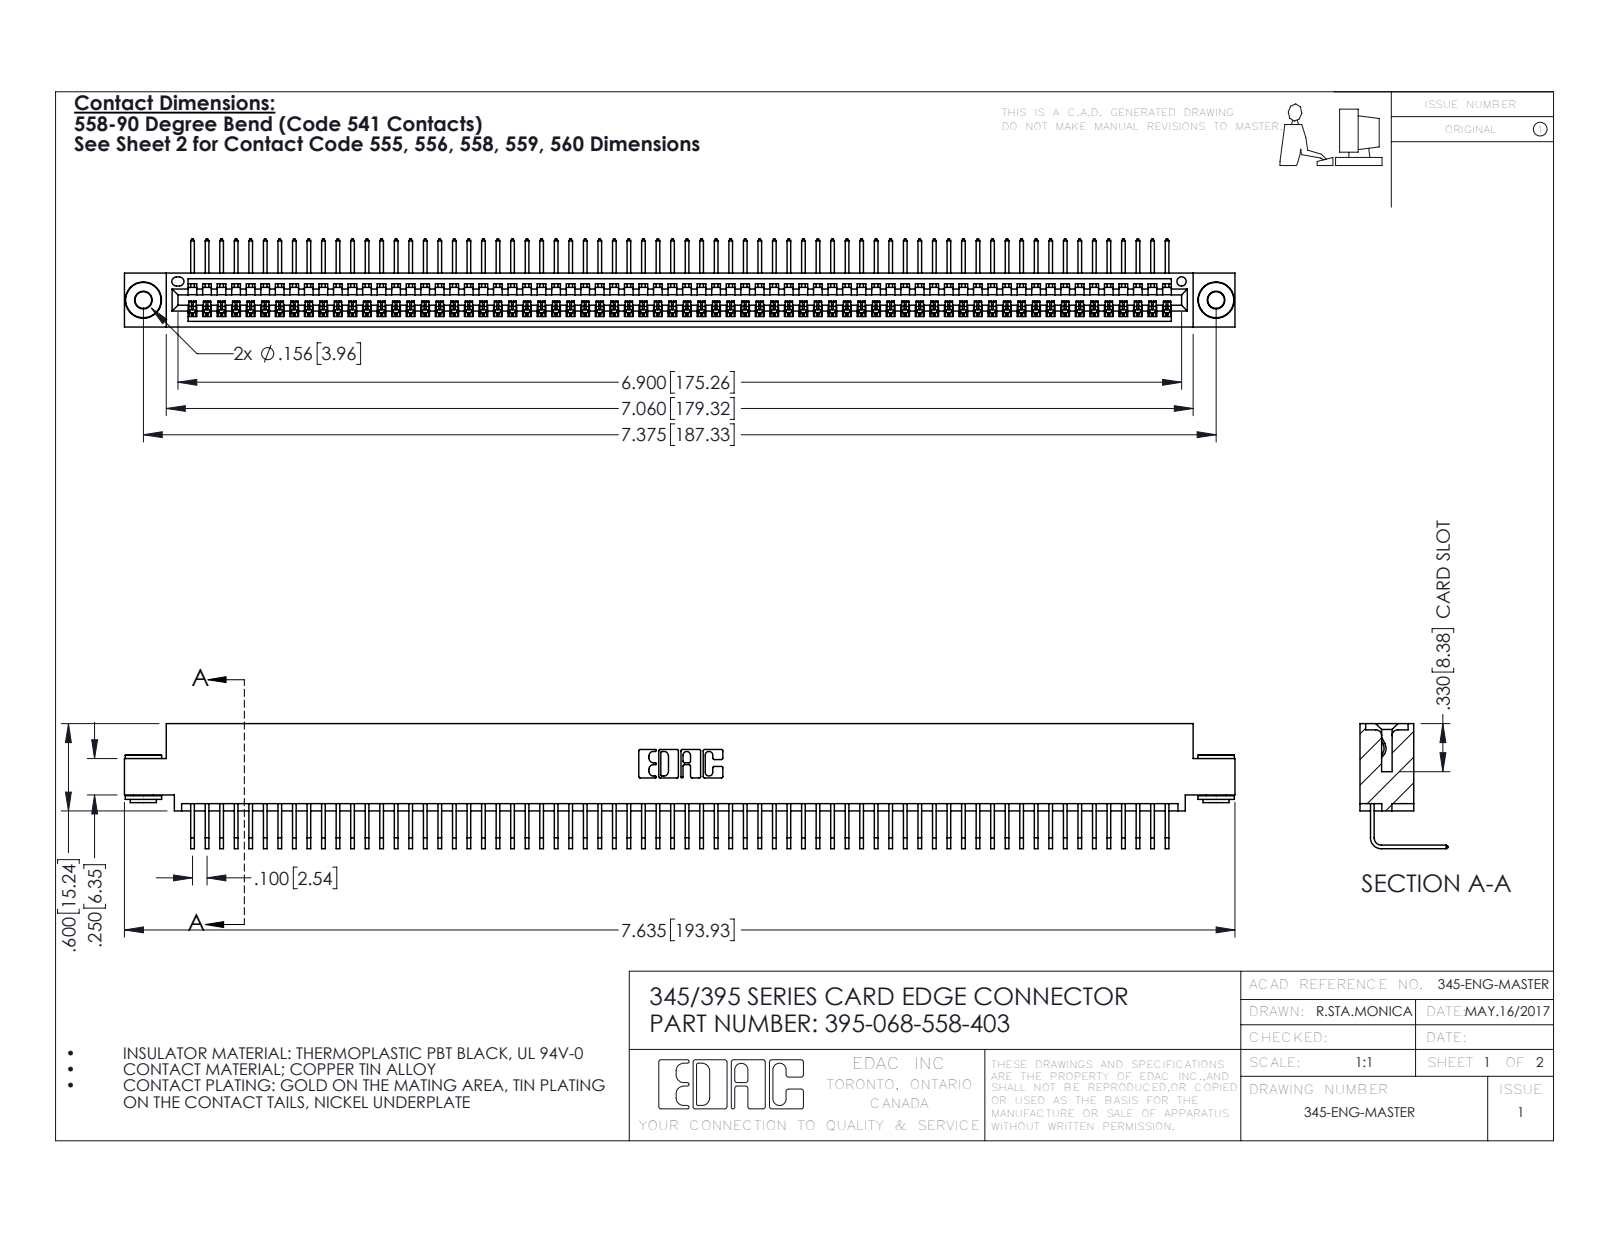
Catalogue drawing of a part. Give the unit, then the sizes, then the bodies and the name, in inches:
Units: inches
Overall size (bounding box): 7.635 × 0.859 × 0.605
Round holes (diameter × count): ⌀0.116 ×2, ⌀0.156 ×2, ⌀0.064 ×1
Round bosses / shafts (diameter × count): ⌀0.25 ×2, ⌀0.18 ×2, ⌀0.136 ×2
Partial cylindrical surfaces — rounded edges, fillets, slot ends (radius × count): R0.006 ×136, R0.01 ×22, R0.007 ×6, R0.031 ×6, R0.026 ×3, R0.031 ×2, R0.04 ×2, R0.014 ×1
Main face-to-face distances: 0.072, 0.298, 0.37, 0.2, 0.025, 0.098, 0.272, 0.225, 0.149, 0.072
Hole centre spacings: 0.27, 7.139, 7.375
Volume: 1.148 in³ · Surface area: 41.81 in²
Bodies: 71 solids, 4248 faces (2950 planar, 1290 cylindrical, 8 other)
Part name (STEP PRODUCT): 345-250-002_345-250-002-102; 345-292-001_558 Tail - 2; 345 Part_0.110 Offset - 0.156 Dia-TH; 395-068-558-403
STEP written by: SolidWorks 2016 (CONFIG_CONTROL_DESIGN)
